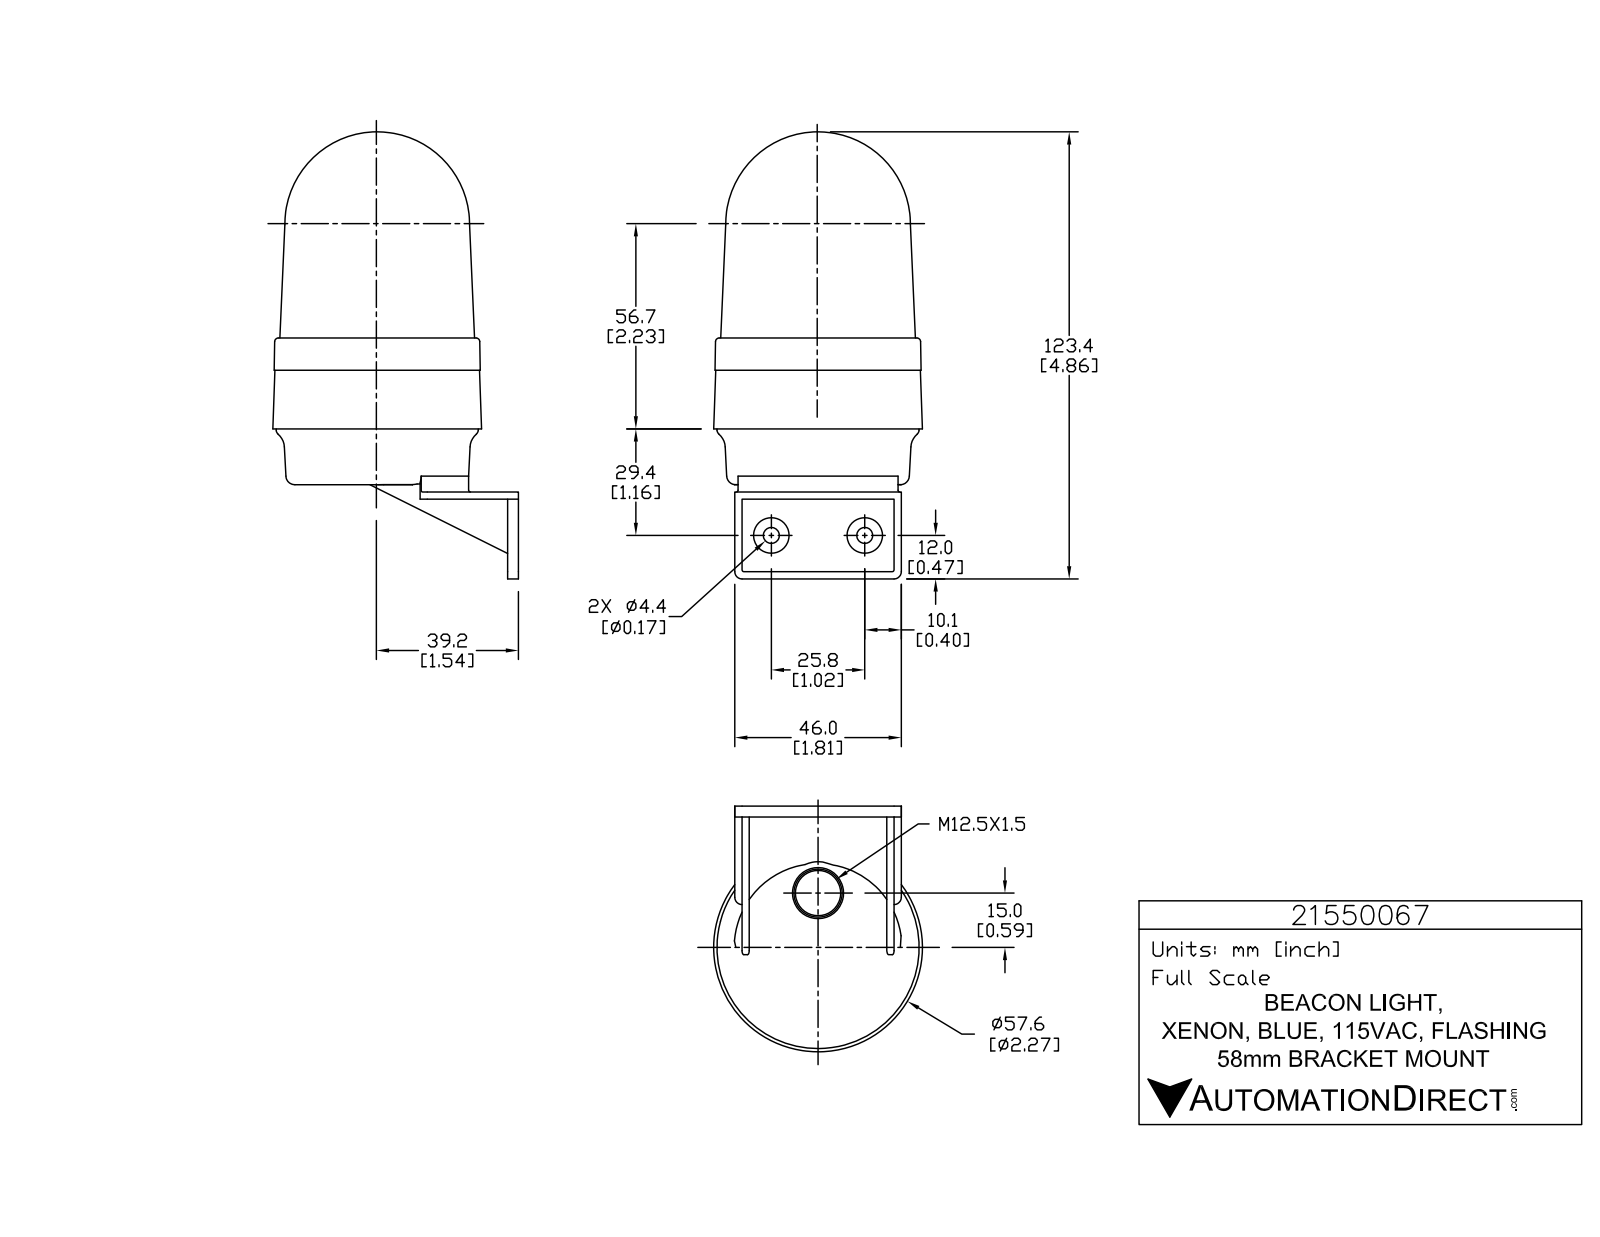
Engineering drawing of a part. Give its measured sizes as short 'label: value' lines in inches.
name: 21550067
written by: SolidWorks 2015 (AUTOMOTIVE_DESIGN)
unit: in
bodies: 1 solid, 828 faces (551 planar, 179 cylindrical, 98 other)
size: 4.858 × 2.852 × 2.407
volume: 12.43 in³; area: 37.49 in²
holes: 3× ⌀0.039, 2× ⌀0.173
bosses: 3× ⌀0.226, 3× ⌀0.056, 2× ⌀0.386, 1× ⌀2.197
rounds: 6× R0.008, 6× R0.008, 6× R0.008, 6× R0.02, 6× R0.131, 4× R0.079, 3× R0.004, 3× R0.005
face distances: 0.079, 0.157, 1.575, 1.654, 0.039, 0.118, 1.496, 0.866, 0.945, 0.764
hole spacings: 1.016
